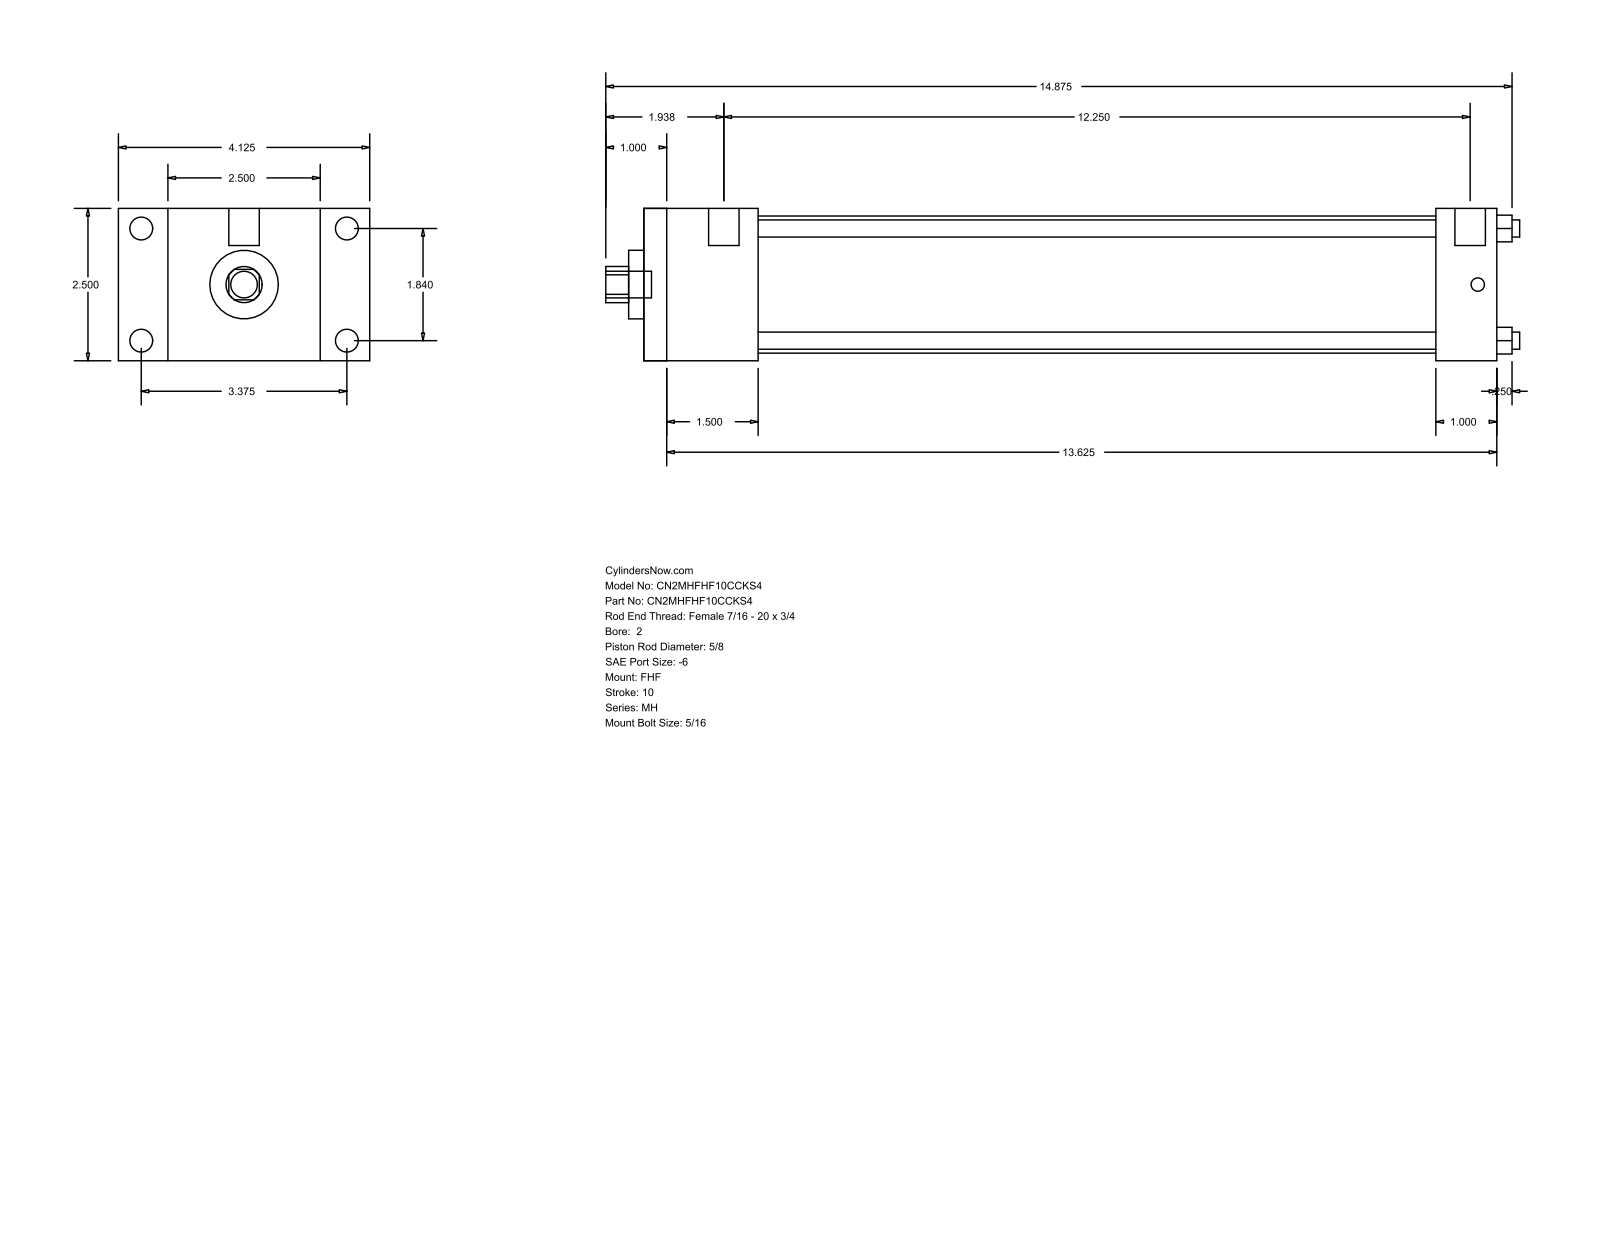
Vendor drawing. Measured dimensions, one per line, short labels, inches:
name: MH_FHF__0200_0.625
written by: GSSL Pune (CONFIG_CONTROL_DESIGN)
unit: in
bodies: 0 solids, 88 faces (60 planar, 28 cylindrical, 0 other)
size: 15 × 4.125 × 2.5
holes: 4× ⌀0.281, 1× ⌀0.625, 1× ⌀1.125, 1× ⌀2.25
bosses: 4× ⌀0.375, 4× ⌀0.219, 2× ⌀0.5, 1× ⌀0.437
rounds: 1× R0.297
face distances: 2.5, 1.875, 14, 12.125, 0.813, 3.313, 4.125, 13, 11.125, 1
hole spacings: 1.301, 1.84, 2.602
